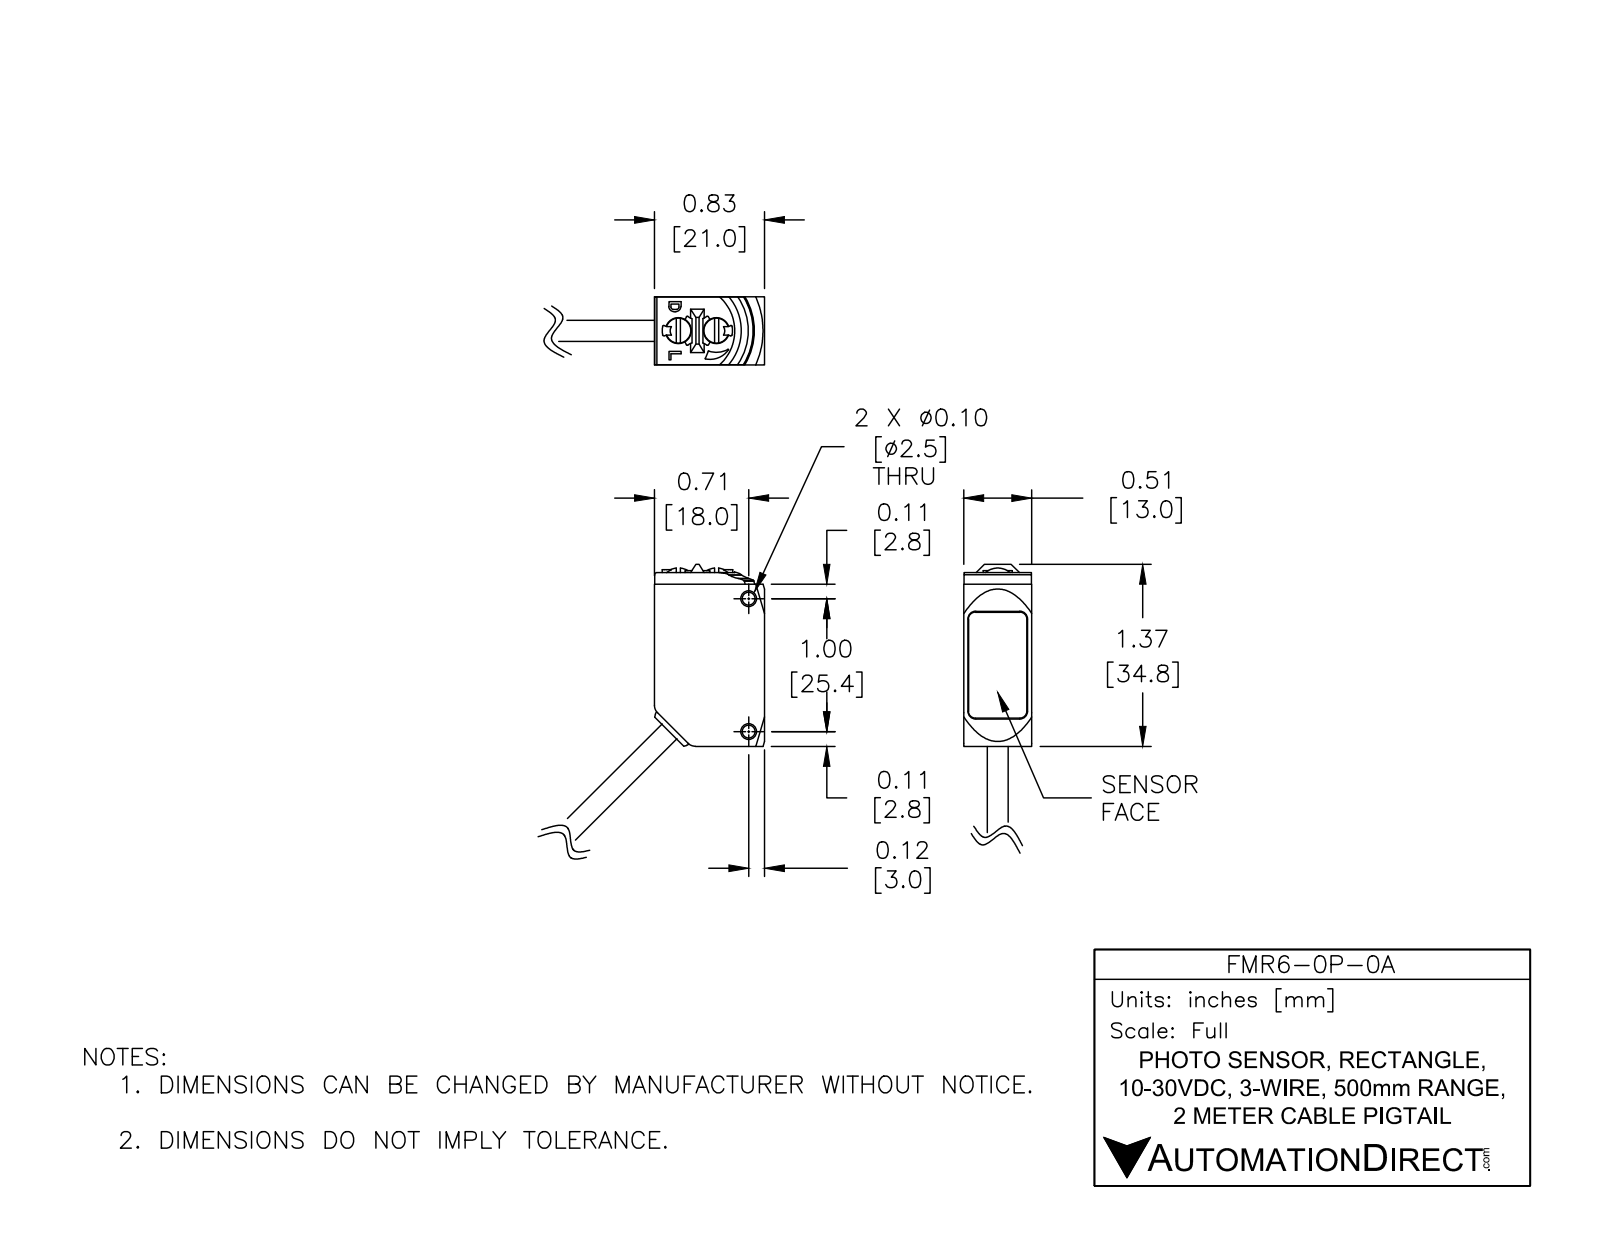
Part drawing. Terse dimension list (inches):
name: FMR6-0P-0A
written by: SolidWorks 2017 (AUTOMOTIVE_DESIGN)
unit: in
bodies: 1 solid, 197 faces (89 planar, 79 cylindrical, 29 other)
size: 1.626 × 0.827 × 0.512
volume: 0.527 in³; area: 5.26 in²
holes: 2× ⌀0.097, 2× ⌀0.197, 1× ⌀0.228
bosses: 2× ⌀0.189, 1× ⌀0.267
rounds: 7× R0.018, 7× R0.02, 5× R0.039, 4× R0.008, 4× R0.01, 4× R0.051, 4× R0.059, 3× R0.004
face distances: 0.512, 0.827, 1.307, 0.51, 0.031, 0.48, 0.037, 0.035, 0.474, 0.03
hole spacings: 0.026, 0.262, 0.287, 1
